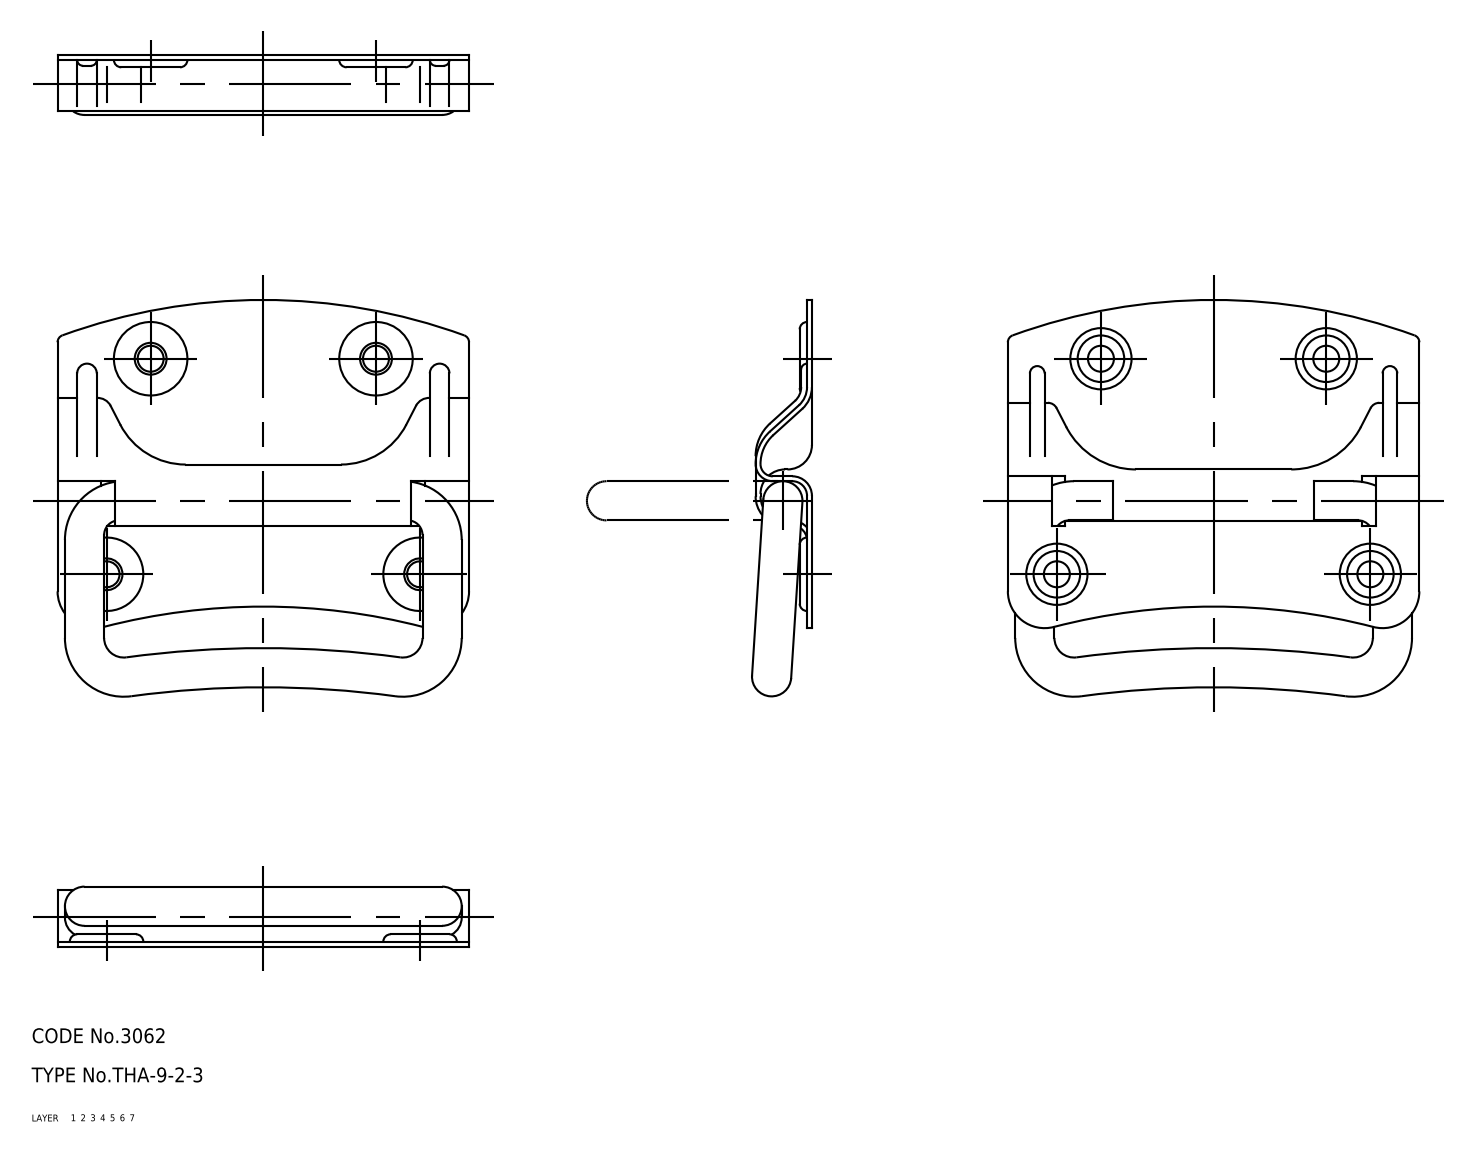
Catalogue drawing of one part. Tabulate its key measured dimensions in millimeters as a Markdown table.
| quantity | value |
| --- | --- |
| part name | grip; base; THA_9_2_3_3650_36 |
| STEP written by | CADfix (AUTOMOTIVE_DESIGN) |
| units | millimeters |
| bodies | 2 solids, 260 faces (0 planar, 0 cylindrical, 260 other) |
| overall size | 84 × 81 × 12.24 |
| volume | 14 593 mm³ |
| surface area | 17 505 mm² |
